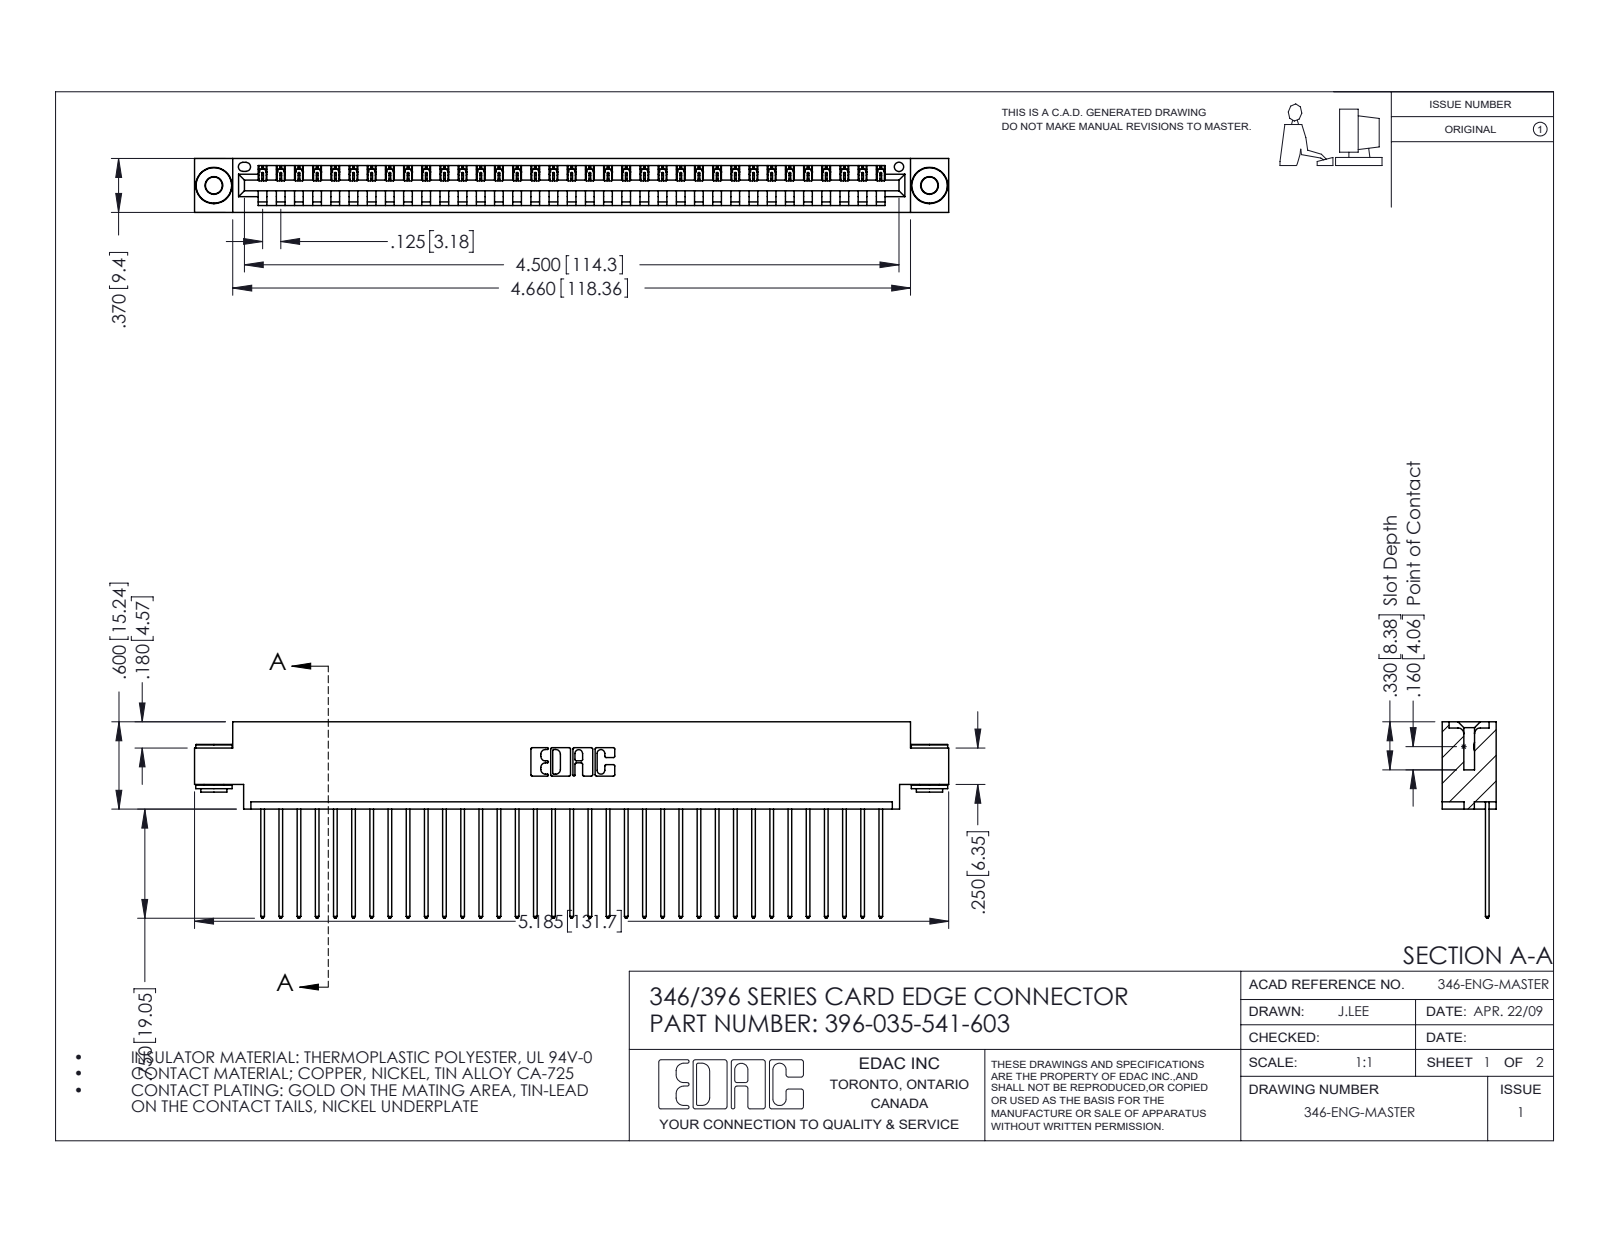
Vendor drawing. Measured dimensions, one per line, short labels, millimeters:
name: 345-250-002_345-250-002-102; 396-035-541-603; 346 Part_0.170 Offset - 0.156 Dia-TH; 345-292-001_345-293-141
written by: SolidWorks 2016 (CONFIG_CONTROL_DESIGN)
unit: mm
bodies: 38 solids, 2194 faces (1490 planar, 696 cylindrical, 8 other)
size: 131.7 × 34.3 × 9.4
volume: 12 500 mm³; area: 16 660 mm²
holes: 2× ⌀2.9, 2× ⌀4, 1× ⌀1.6
bosses: 2× ⌀6.4, 2× ⌀4.6, 2× ⌀3.5
rounds: 70× R0.2, 70× R0.3, 22× R0.3, 6× R0.2, 6× R0.8, 3× R0.7, 2× R0.8, 2× R1
face distances: 1.2, 8.2, 9.4, 6.4, 0.6, 1.8, 7.6, 3.8, 5.6, 2.5
hole spacings: 6.2, 119.7, 125
